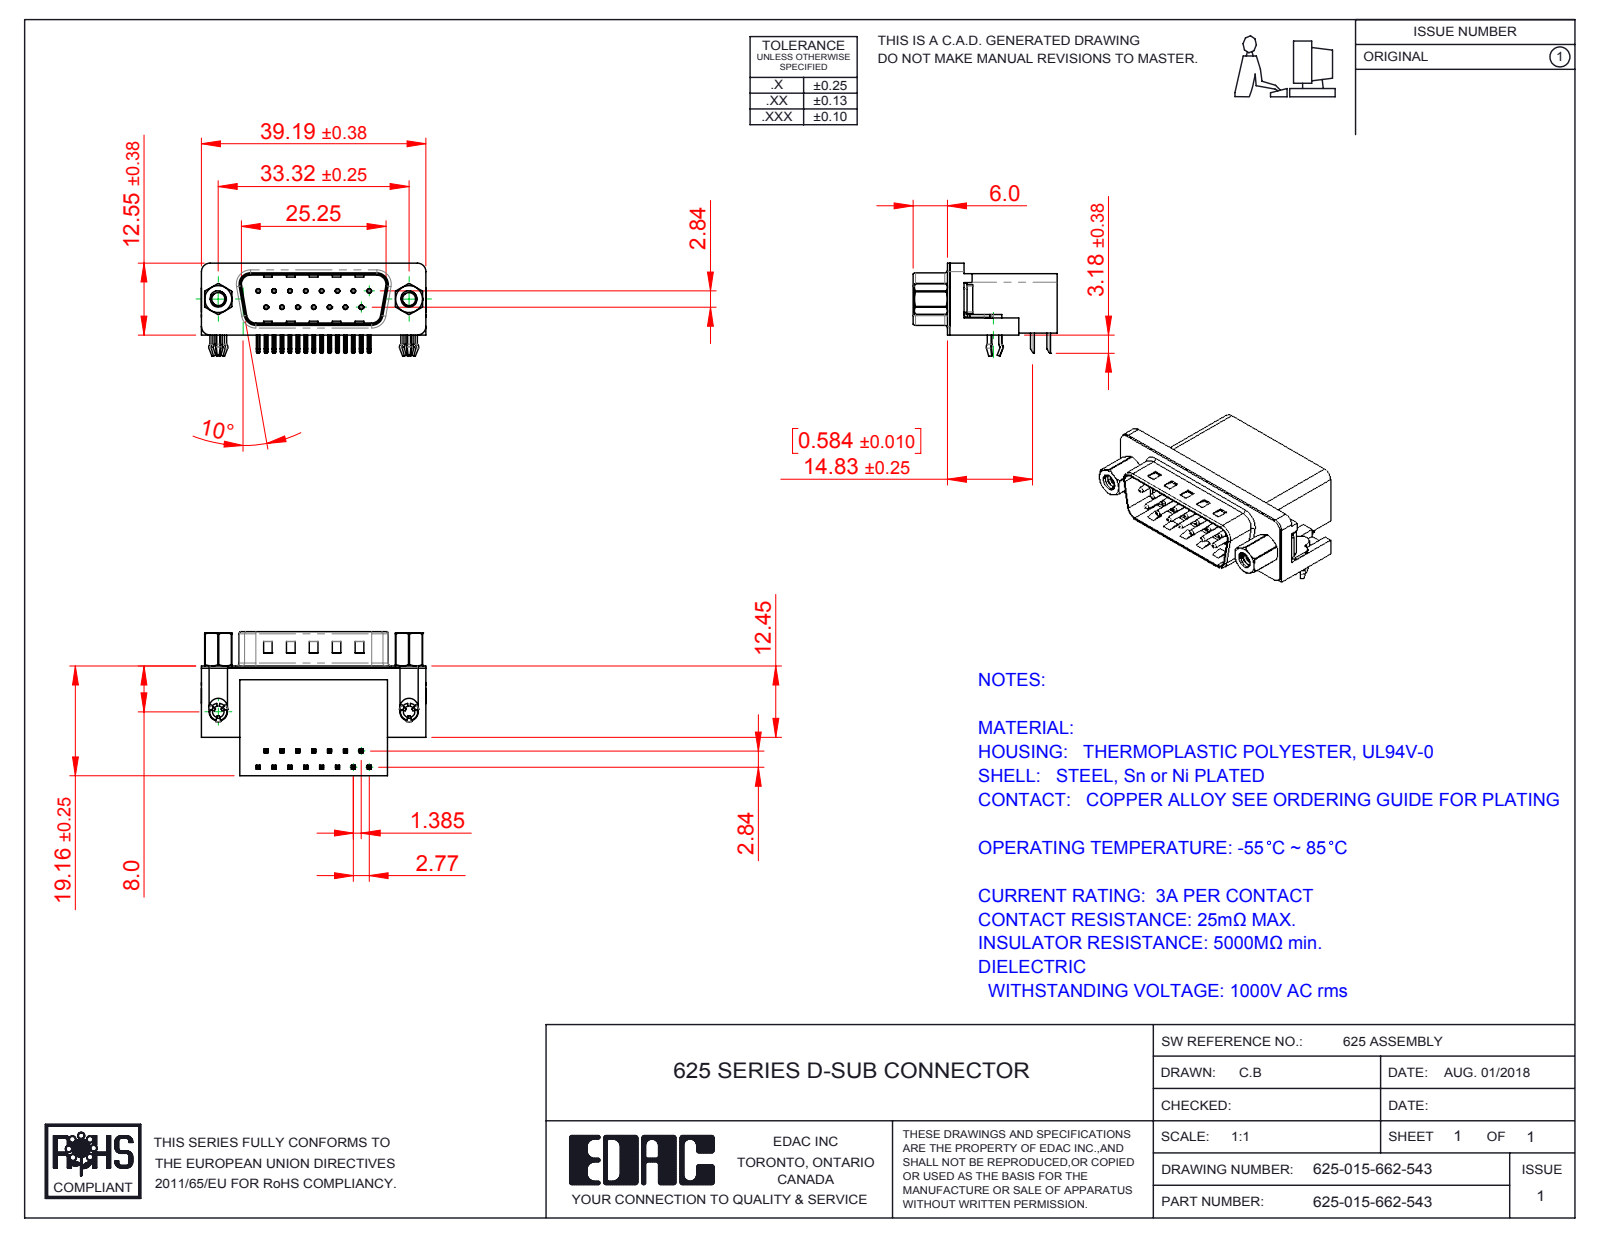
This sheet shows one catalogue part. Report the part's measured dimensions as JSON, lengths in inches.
{"part_name": "625 3 Prong Board Lock; 625 Contact Top; 625 Shell_15 Socket; 625 4-40 Hex Standoff 5 (+4 more)", "step_written_by": "SolidWorks 2016 (CONFIG_CONTROL_DESIGN)", "units": "inches", "bodies": {"solids": 23, "faces": 1709, "planar": 953, "cylindrical": 525, "other": 231}, "overall_size": [1.544, 0.991, 0.64], "volume_in3": 0.395, "surface_area_in2": 10.8, "round_holes": [[0.014, 15], [0.031, 15], [0.079, 2], [0.089, 2], [0.09, 2], [0.157, 2], [0.189, 2], [0.197, 2]], "round_bosses_or_shafts": [[0.03, 15], [0.193, 2], [0.187, 2], [0.154, 2], [0.118, 2], [0.11, 2]], "partial_cylinders_radius": [[0.01, 72], [0.005, 30], [0.039, 16], [0.02, 9], [0.063, 8], [0.059, 6], [0.035, 4], [0.079, 4]], "face_to_face_distances": [0.016, 0.407, 0.739, 0.083, 0.754, 0.412, 0.067, 0.428, 0.345, 0.64], "hole_center_spacings": [0.124, 0.109, 0.218, 0.327, 0.436, 0.198, 0.198, 0.294]}
